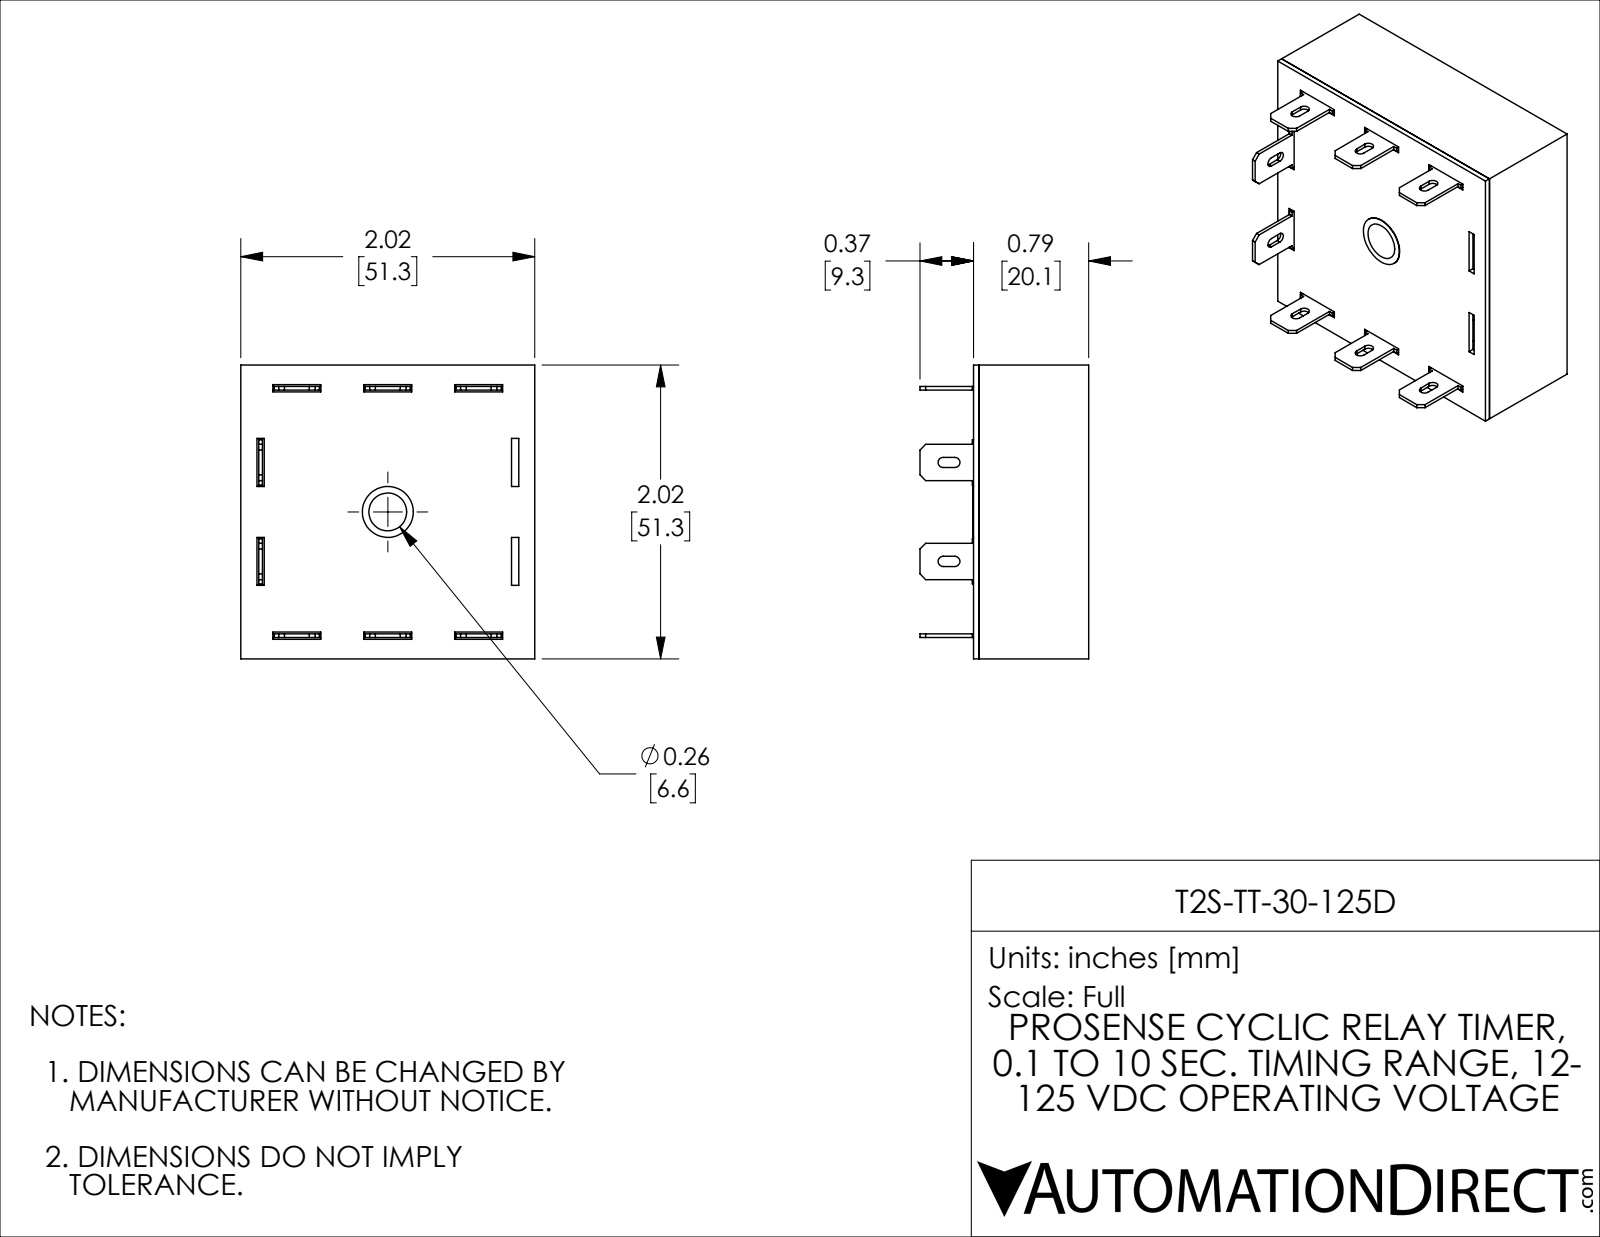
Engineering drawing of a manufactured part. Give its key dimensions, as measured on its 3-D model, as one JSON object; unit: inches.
{"part_name": "T2S-TT-30-125D", "step_written_by": "SolidWorks 2021 (CONFIG_CONTROL_DESIGN)", "units": "inches", "bodies": {"solids": 10, "faces": 256, "planar": 234, "cylindrical": 20, "other": 2}, "overall_size": [2.02, 2.02, 1.16], "volume_in3": 0.674, "surface_area_in2": 35.37, "round_holes": [[0.35, 1]], "partial_cylinders_radius": [[0.035, 10]], "face_to_face_distances": [0.045, 1.975, 0.754, 0.792, 0.038, 0.709, 0.747, 2.02, 1.93, 0.147]}
